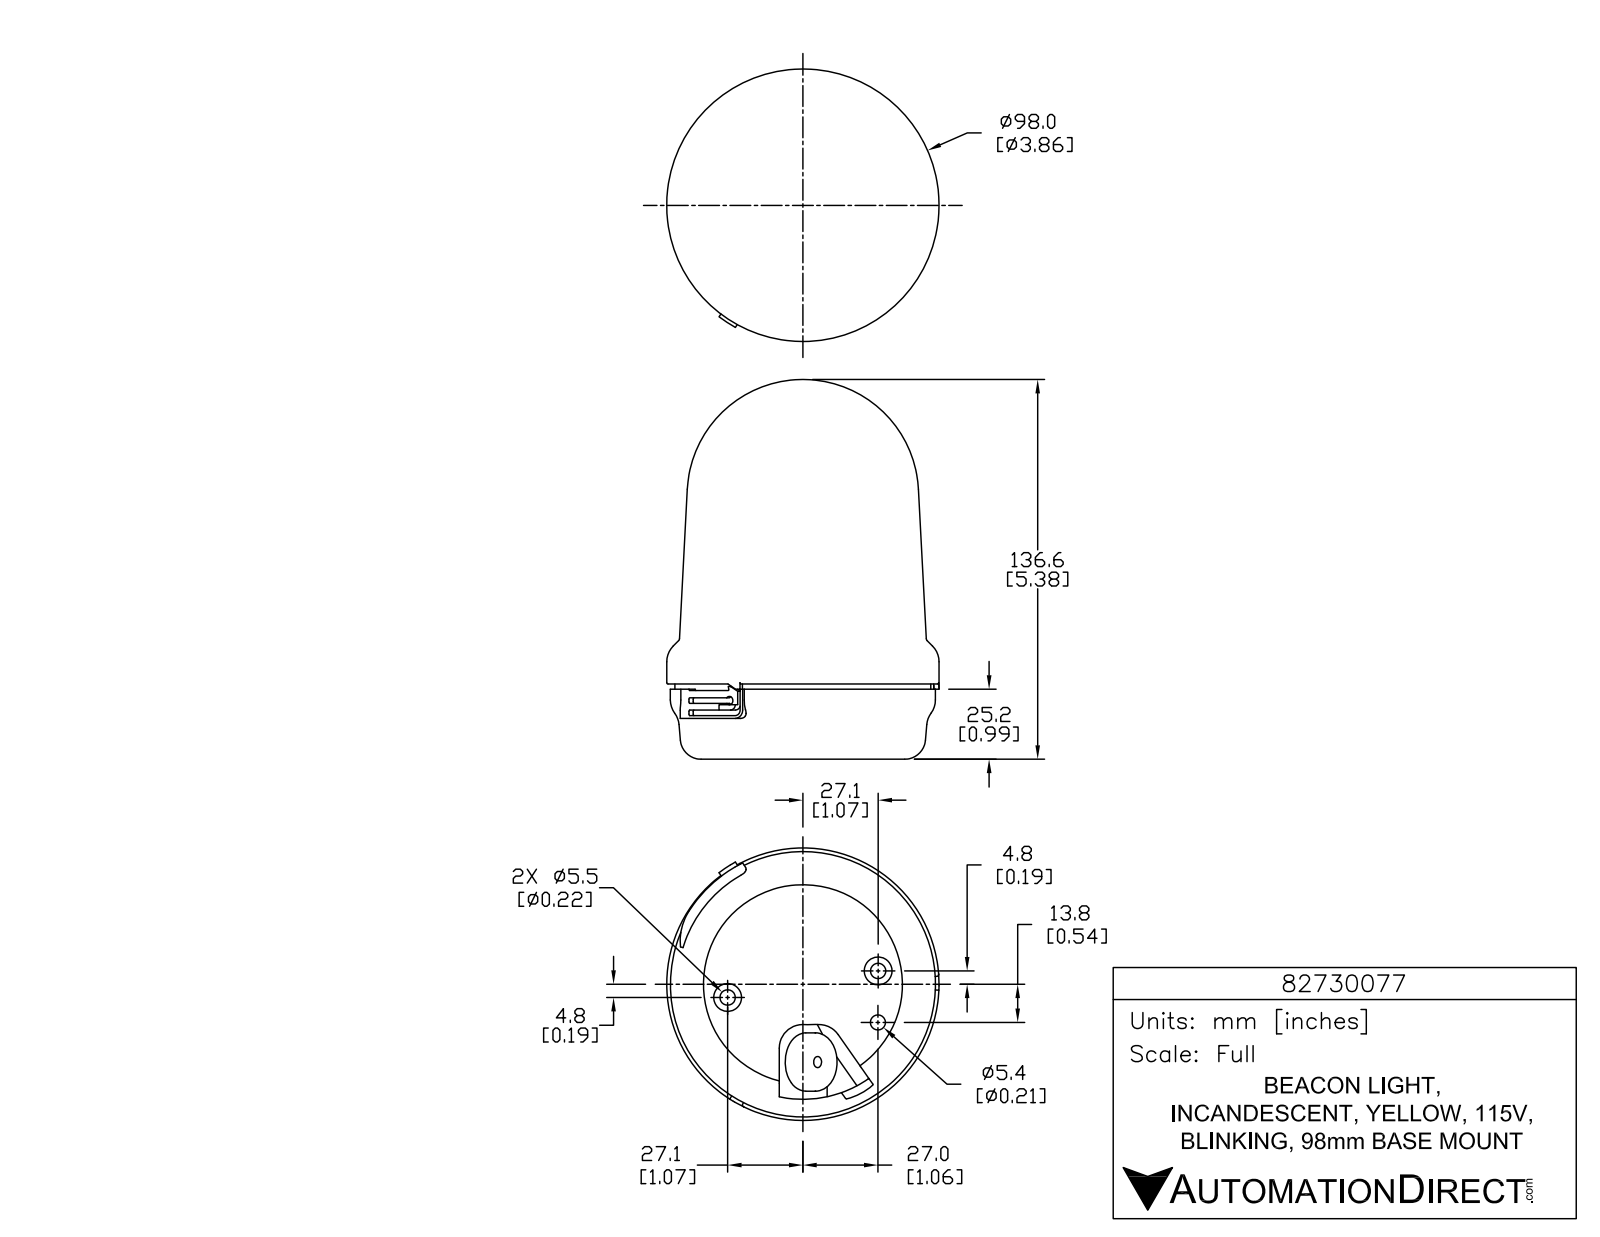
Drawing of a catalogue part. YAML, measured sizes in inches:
part_name: "82730077"
step_written_by: "SolidWorks 2015 (AUTOMOTIVE_DESIGN)"
units: inches
bodies: {solids: 1, faces: 872, planar: 566, cylindrical: 204, other: 102}
overall_size: [5.378, 3.858, 3.858]
volume: 44.69
surface_area: 73.66
round_holes:
  - {diameter: 0.059, count: 3}
  - {diameter: 0.217, count: 2}
  - {diameter: 0.157, count: 1}
  - {diameter: 0.213, count: 1}
  - {diameter: 2.819, count: 1}
round_bosses_or_shafts:
  - {diameter: 0.339, count: 3}
  - {diameter: 0.084, count: 3}
  - {diameter: 0.394, count: 2}
  - {diameter: 3.858, count: 1}
  - {diameter: 3.756, count: 1}
  - {diameter: 3.626, count: 1}
  - {diameter: 0.827, count: 1}
partial_cylinders:
  - {radius: 0.005, count: 9}
  - {radius: 0.005, count: 6}
  - {radius: 0.012, count: 6}
  - {radius: 0.012, count: 6}
  - {radius: 0.012, count: 6}
  - {radius: 0.196, count: 6}
  - {radius: 0.02, count: 5}
  - {radius: 0.039, count: 4}
face_to_face_distances: [1.045, 0.972, 0.073, 0.02, 0.992, 1.065, 0.236, 0.579, 0.559, 0.413]
hole_center_spacings: [1.083, 0.73, 1.193, 2.158, 2.165]
